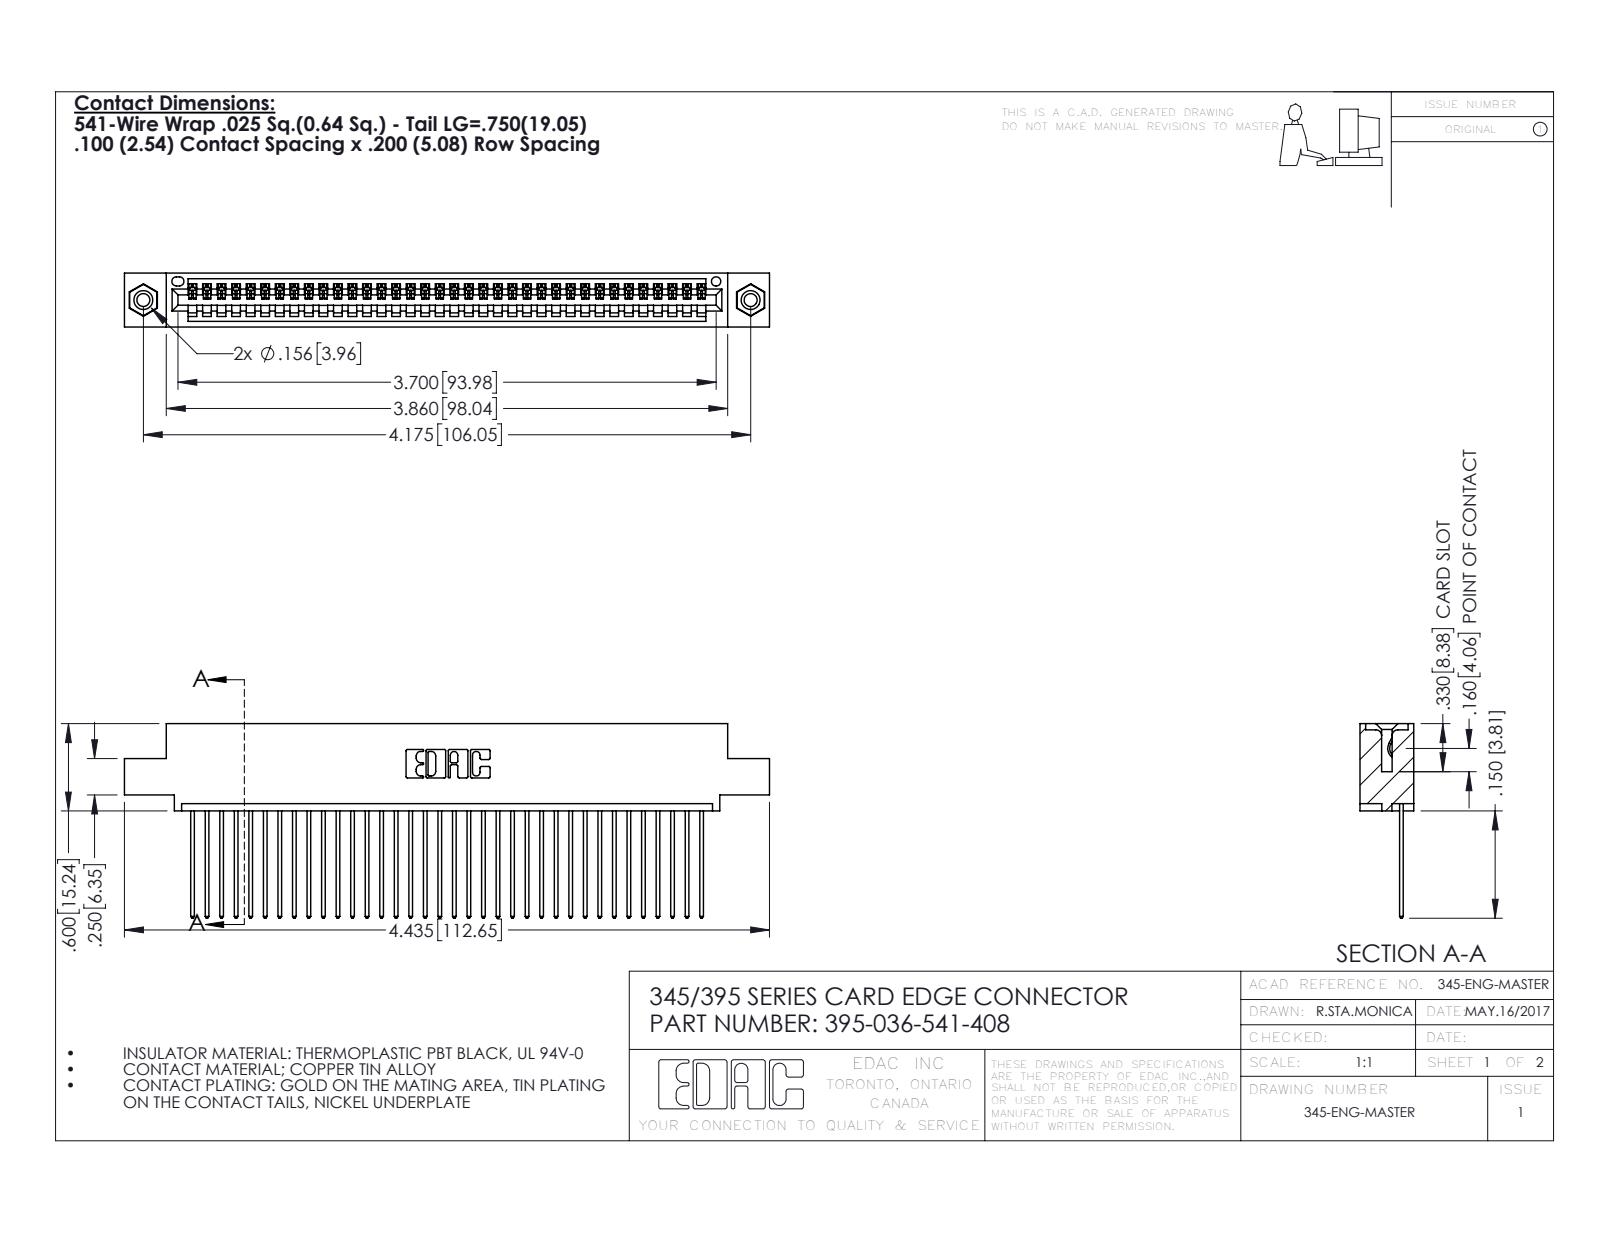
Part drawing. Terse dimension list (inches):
name: 345-292-001_345-293-141; 395-036-541-408; 345-250-001_345-250-003-102; 345 Part_0.110 Offset - 0.156 Dia-TI
written by: SolidWorks 2016 (CONFIG_CONTROL_DESIGN)
unit: in
bodies: 39 solids, 2278 faces (1556 planar, 706 cylindrical, 16 other)
size: 4.435 × 1.337 × 0.37
volume: 0.652 in³; area: 23.13 in²
holes: 2× ⌀0.089, 2× ⌀0.125, 2× ⌀0.156, 1× ⌀0.064
bosses: 2× ⌀0.155
rounds: 72× R0.006, 72× R0.01, 22× R0.01, 6× R0.007, 6× R0.031, 3× R0.026, 2× R0.031, 2× R0.04
face distances: 0.072, 0.298, 0.098, 0.272, 0.025, 0.37, 0.2, 0.225, 0.149, 0.072
hole spacings: 0.27, 3.939, 4.175
